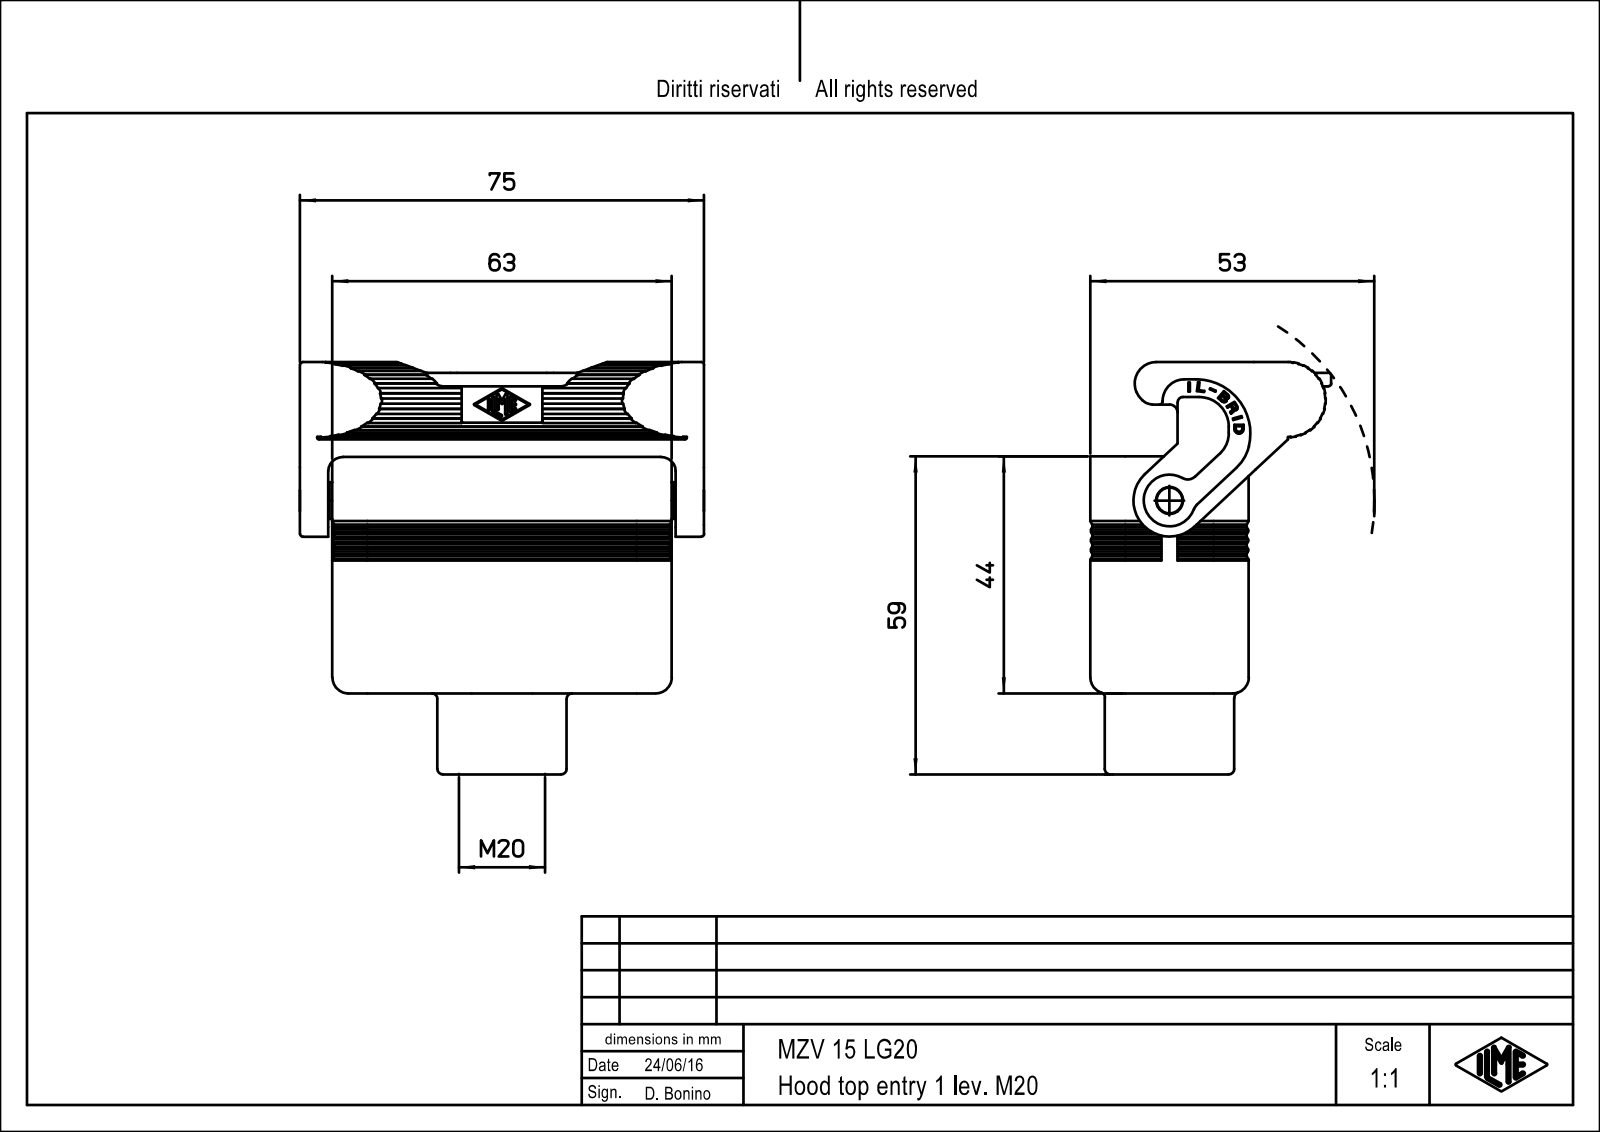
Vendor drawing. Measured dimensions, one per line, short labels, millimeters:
name: MZV_15_LG20
written by: PTC Creo Elements/Direct Modeling 19.0E 27-Jun-2016 (C) Parametric Technology GmbH (AUTOMOTIVE_DESIGN)
unit: mm
bodies: 1 solid, 857 faces (515 planar, 226 cylindrical, 116 other)
size: 76.5 × 75.05 × 44.7
volume: 41 617 mm³; area: 27 836 mm²
holes: 4× ⌀3, 1× ⌀5, 1× ⌀16
bosses: 1× ⌀24, 1× ⌀6.8, 1× ⌀4.8, 1× ⌀3.2
rounds: 63× R0.5, 15× R0.2, 8× R3.5, 7× R3, 4× R6.5, 3× R0.1, 2× R0.3, 2× R2
face distances: 2.6, 26.8, 24.2, 29.4, 60.4, 33.2, 30.6, 6.4, 3.8, 2.5
hole spacings: 26.01, 16, 49.5, 52.02
